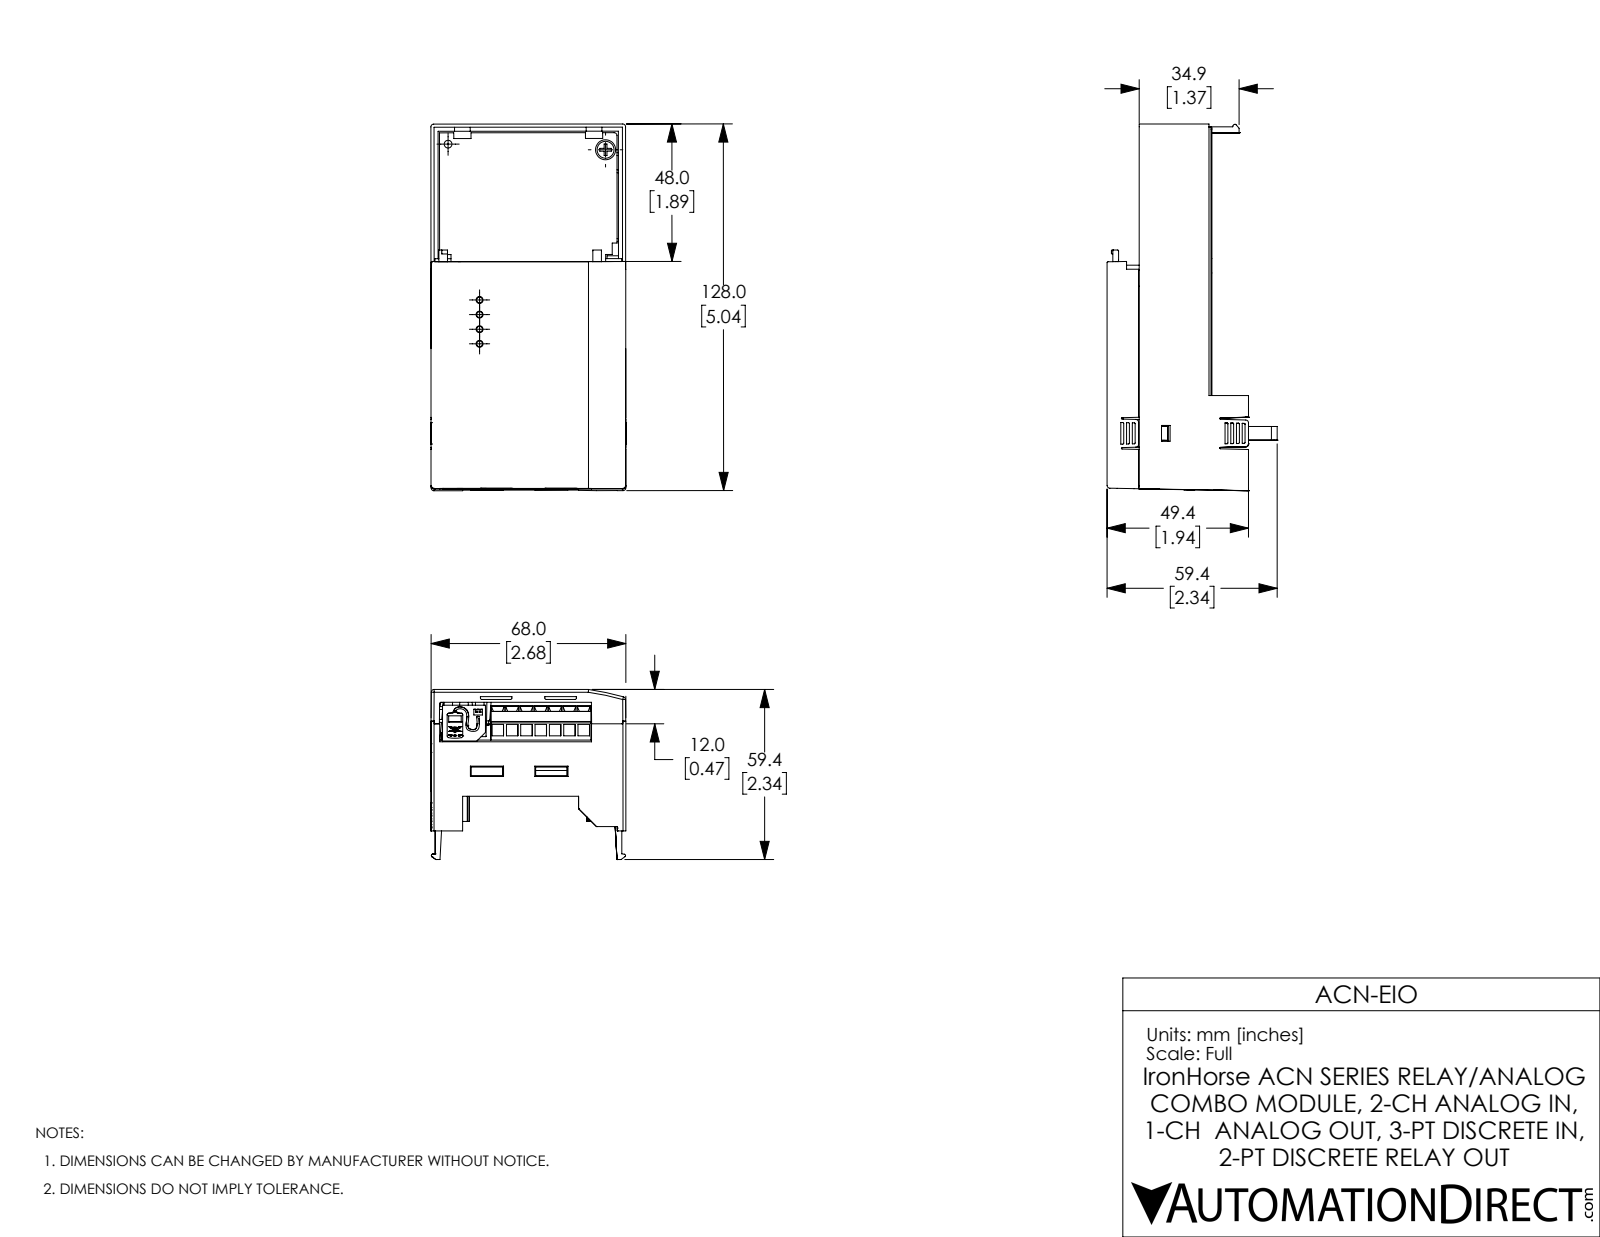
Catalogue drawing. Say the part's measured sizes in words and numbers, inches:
The part is named "S100_OPTION_MODULE_EXT_IO_200525 red1 r1 fXT". Its 3-D file was written by "SolidWorks 2017 (AUTOMOTIVE_DESIGN)". It is 10 solids with 1822 faces: 1274 planar, 410 cylindrical and 138 other. Overall it measures 5.041 by 2.681 by 2.339 inches. Its volume is 4.981 cubic inches and its surface area 124.9 square inches. Round holes: 7 of diameter 0.106, 7 of diameter 0.157, 4 of diameter 0.035, 2 of diameter 0.098, 2 of diameter 0.138. Round bosses or shafts: 11 of diameter 0.098, 7 of diameter 0.051, 4 of diameter 0.031, 2 of diameter 0.315, 2 of diameter 0.276, 2 of diameter 0.232, 2 of diameter 0.118, 1 of diameter 0.106. Partial cylindrical surfaces (rounded edges, fillets, slot ends): 52 of radius 0.039, 45 of radius 0.012, 19 of radius 0.02, 8 of radius 0.008, 8 of radius 0.028, 6 of radius 0.005, 6 of radius 0.01, 6 of radius 0.074. The main face-to-face distances are 0.098, 0.878, 0.063, 0.118, 0.181, 0.217, 0.28, 2.577, 0.976, 0.76. The hole center spacings are 0.197, 0.394, 0.591, 0.787, 0.984, 0.201, 0.402, 1.181.
